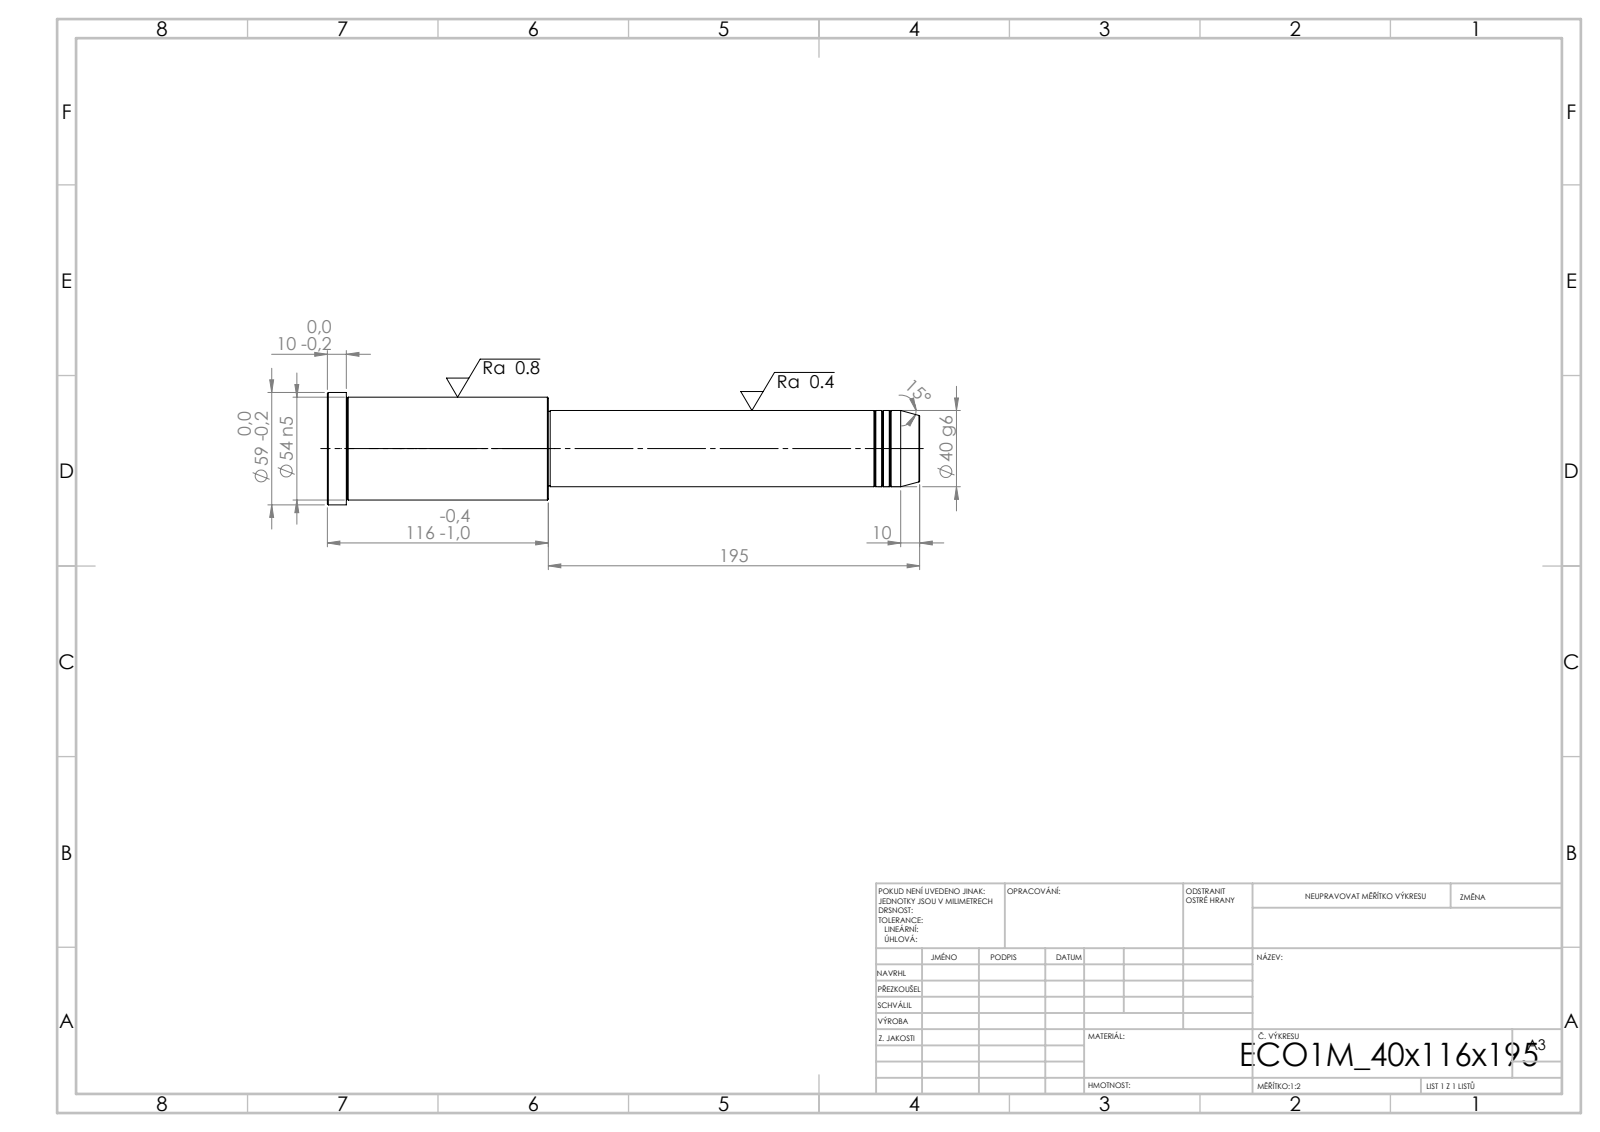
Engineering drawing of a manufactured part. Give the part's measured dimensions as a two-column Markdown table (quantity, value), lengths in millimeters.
| quantity | value |
| --- | --- |
| STEP written by | SolidWorks 2019 (CONFIG_CONTROL_DESIGN) |
| units | millimeters |
| bodies | 1 solid, 43 faces (5 planar, 14 cylindrical, 24 other) |
| overall size | 311 × 59 × 59 |
| volume | 513 217 mm³ |
| surface area | 49 755 mm² |
| round bosses / shafts (diameter × count) | 59 × 1, 54 × 1, 40 × 1, 39 × 1 |
| main face-to-face distances | 116, 195, 311, 301, 106, 10, 194, 1, 107, 117 |
